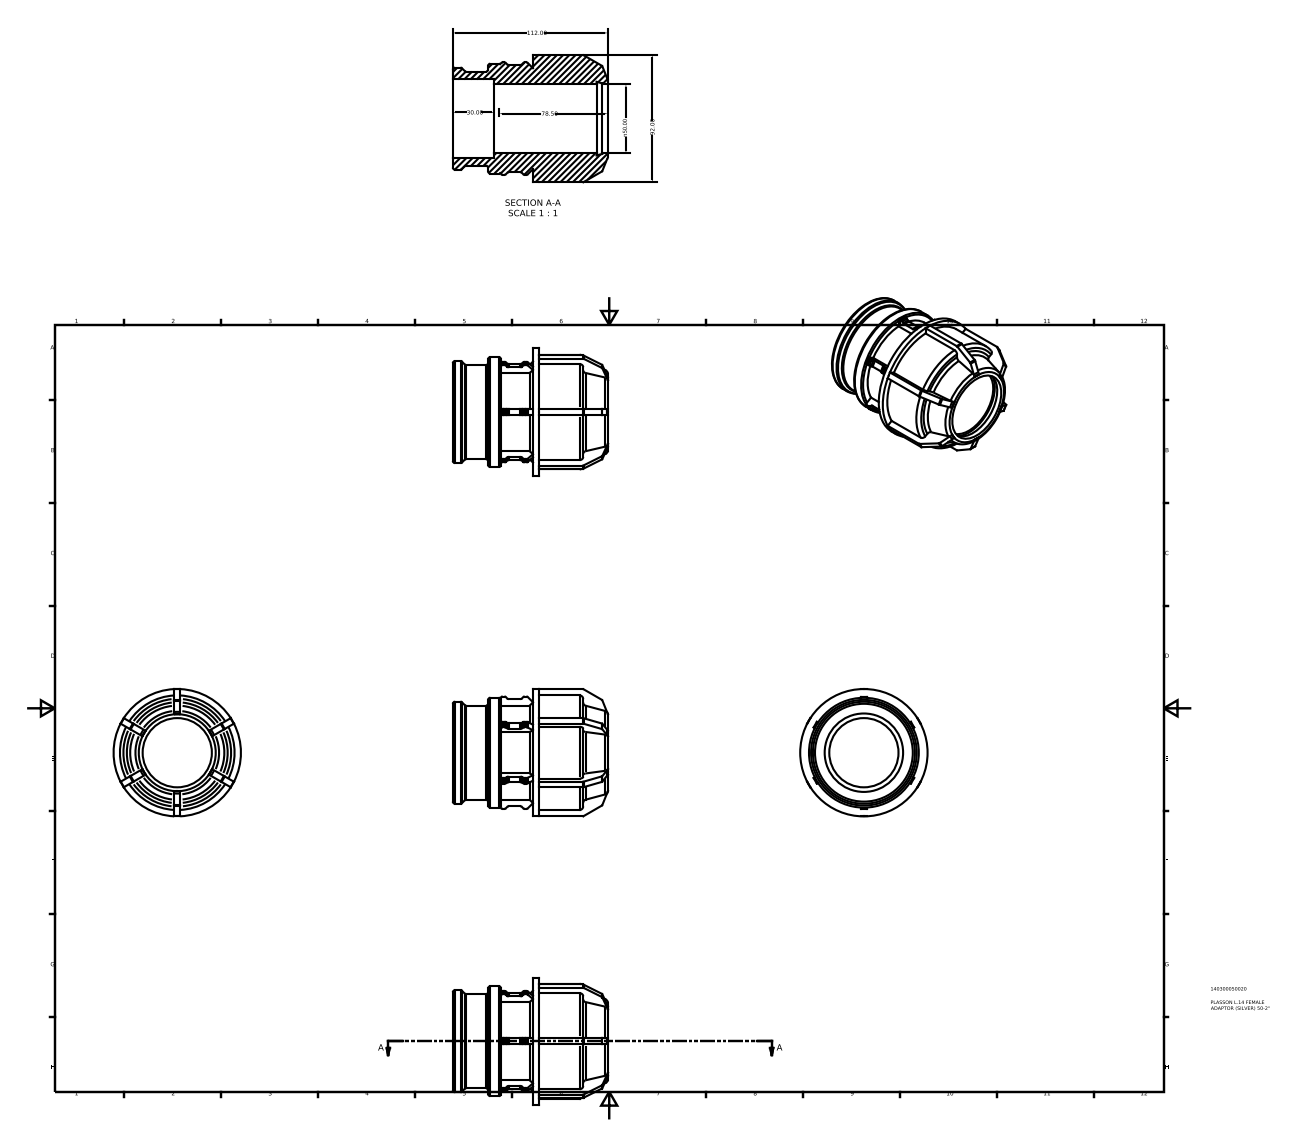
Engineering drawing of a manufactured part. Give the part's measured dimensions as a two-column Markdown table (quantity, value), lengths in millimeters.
| quantity | value |
| --- | --- |
| part name | 140300050020 |
| STEP written by | Autodesk Inventor 2015 (AUTOMOTIVE_DESIGN) |
| units | millimeters |
| bodies | 1 solid, 260 faces (159 planar, 67 cylindrical, 34 other) |
| overall size | 112 × 92 × 92 |
| volume | 259 259 mm³ |
| surface area | 60 059 mm² |
| round holes (diameter × count) | 50 × 1, 56.66 × 1 |
| round bosses / shafts (diameter × count) | 92 × 1, 82.8 × 1, 79.32 × 1, 73.65 × 1, 67.99 × 1 |
| partial cylindrical surfaces (radius × count) | 1.5 × 48 |
| main face-to-face distances | 4.6, 57.88, 4.1, 61.98, 4.5, 34.5, 23.38, 27.48, 25.5, 9 |
